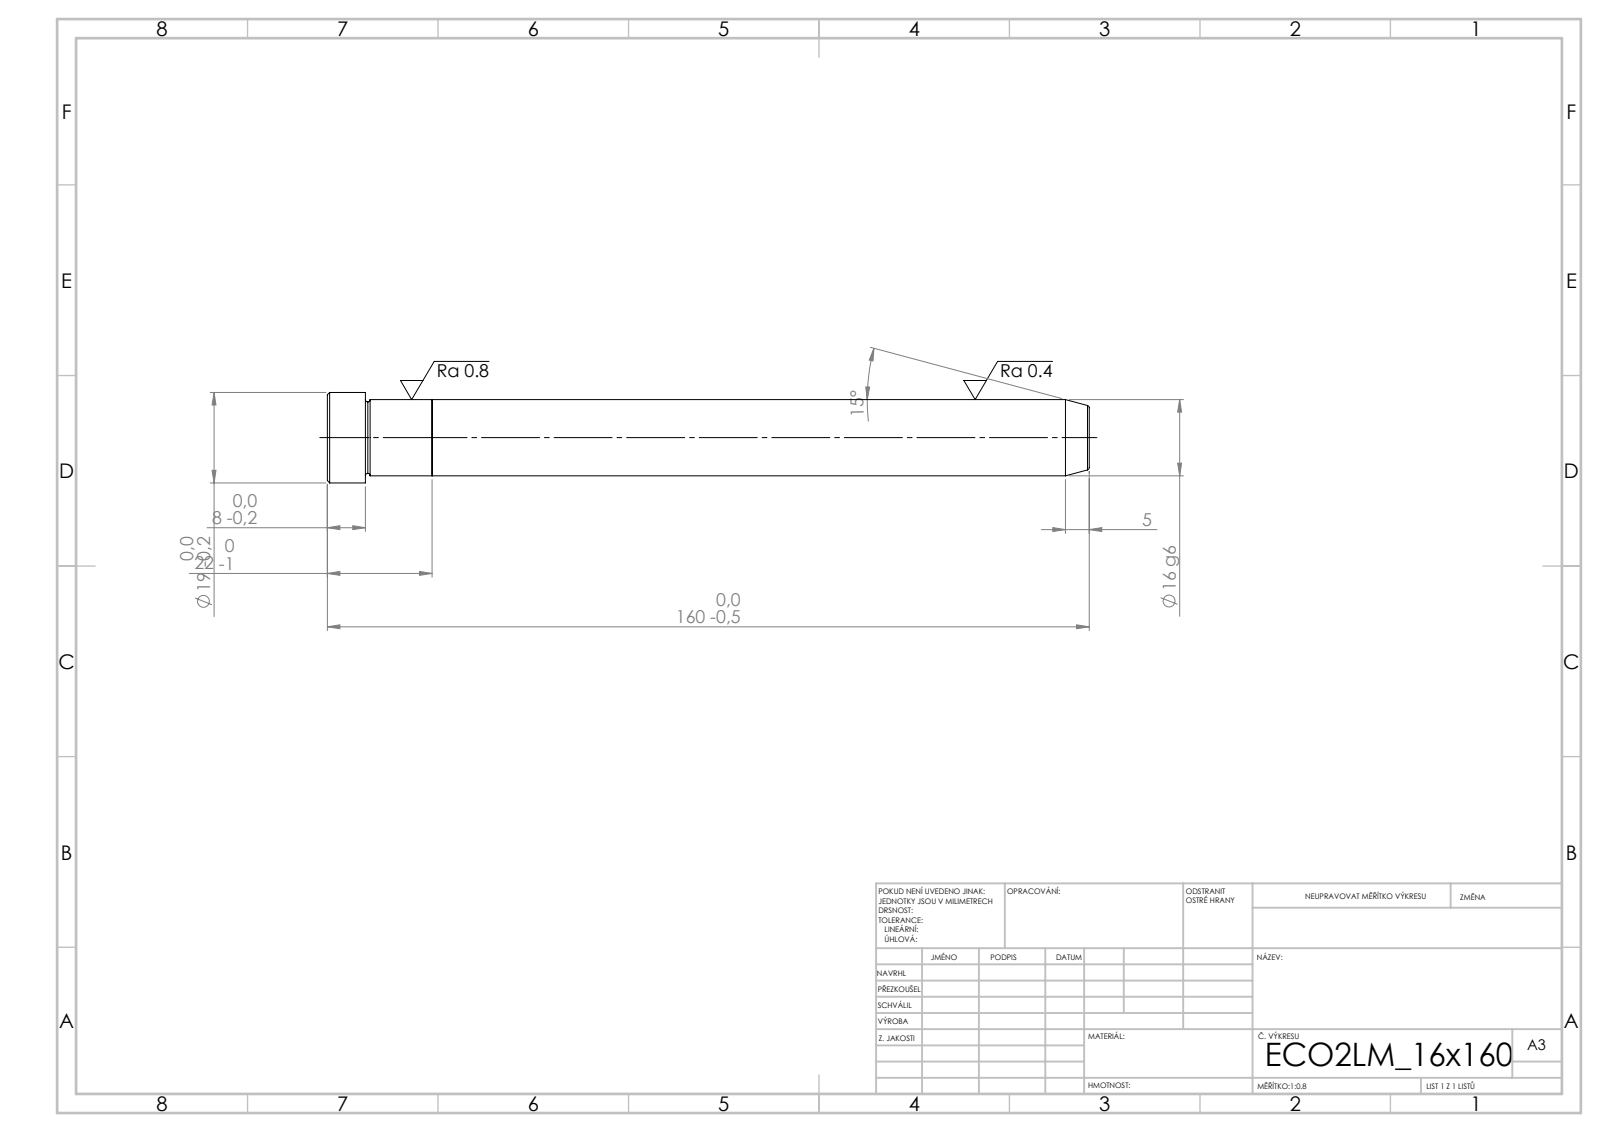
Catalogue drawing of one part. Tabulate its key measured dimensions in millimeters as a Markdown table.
| quantity | value |
| --- | --- |
| STEP written by | SolidWorks 2019 (CONFIG_CONTROL_DESIGN) |
| units | millimeters |
| bodies | 2 solids, 21 faces (5 planar, 6 cylindrical, 10 other) |
| overall size | 160 × 19 × 19 |
| volume | 32 643 mm³ |
| surface area | 9 015 mm² |
| round bosses / shafts (diameter × count) | 19 × 1, 16 × 1 |
| main face-to-face distances | 22, 138, 160, 152, 14, 8 |
